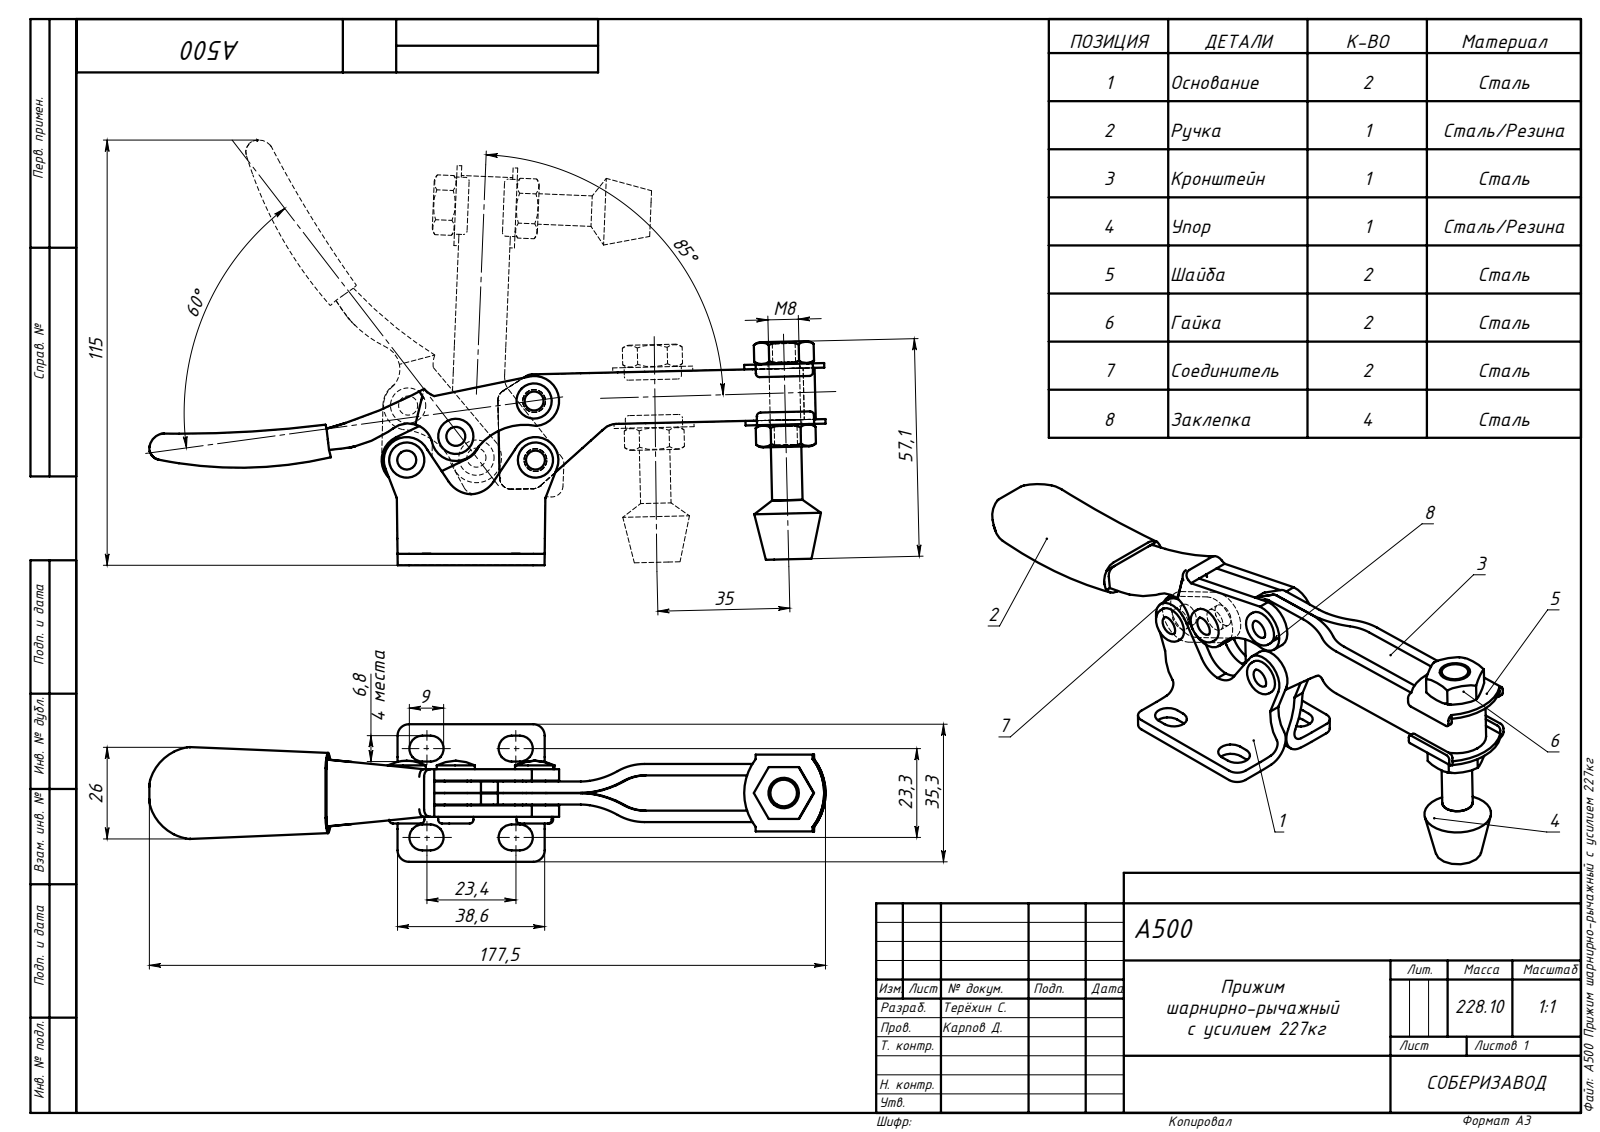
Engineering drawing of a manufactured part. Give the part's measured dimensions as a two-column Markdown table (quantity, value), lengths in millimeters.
| quantity | value |
| --- | --- |
| part name | CH-225D шайба_00; CH-225D основание_00; CH-225D гайка_00; CH-225D заклепка_00 (+5 more) |
| STEP written by | SolidWorks 2020 (AUTOMOTIVE_DESIGN) |
| units | millimeters |
| bodies | 15 solids, 395 faces (137 planar, 173 cylindrical, 85 other) |
| overall size | 177.5 × 58.8 × 36.1 |
| volume | 28 173 mm³ |
| surface area | 30 675 mm² |
| round holes (diameter × count) | 6 × 6, 8.5 × 2 |
| round bosses / shafts (diameter × count) | 10 × 4, 9.25 × 4, 8 × 1 |
| partial cylindrical surfaces (radius × count) | 3 × 12, 3.4 × 8, 1 × 4, 1.2 × 4, 14.63 × 4, 2.66 × 2, 4.62 × 2, 5.66 × 2 |
| main face-to-face distances | 3, 4.6, 7.65, 6.05, 1.6, 10.65, 3.05, 3.22, 6.27, 6.28 |
| hole center spacings | 14.3, 15.5, 21.81, 22.55, 33.78, 36.85 |
